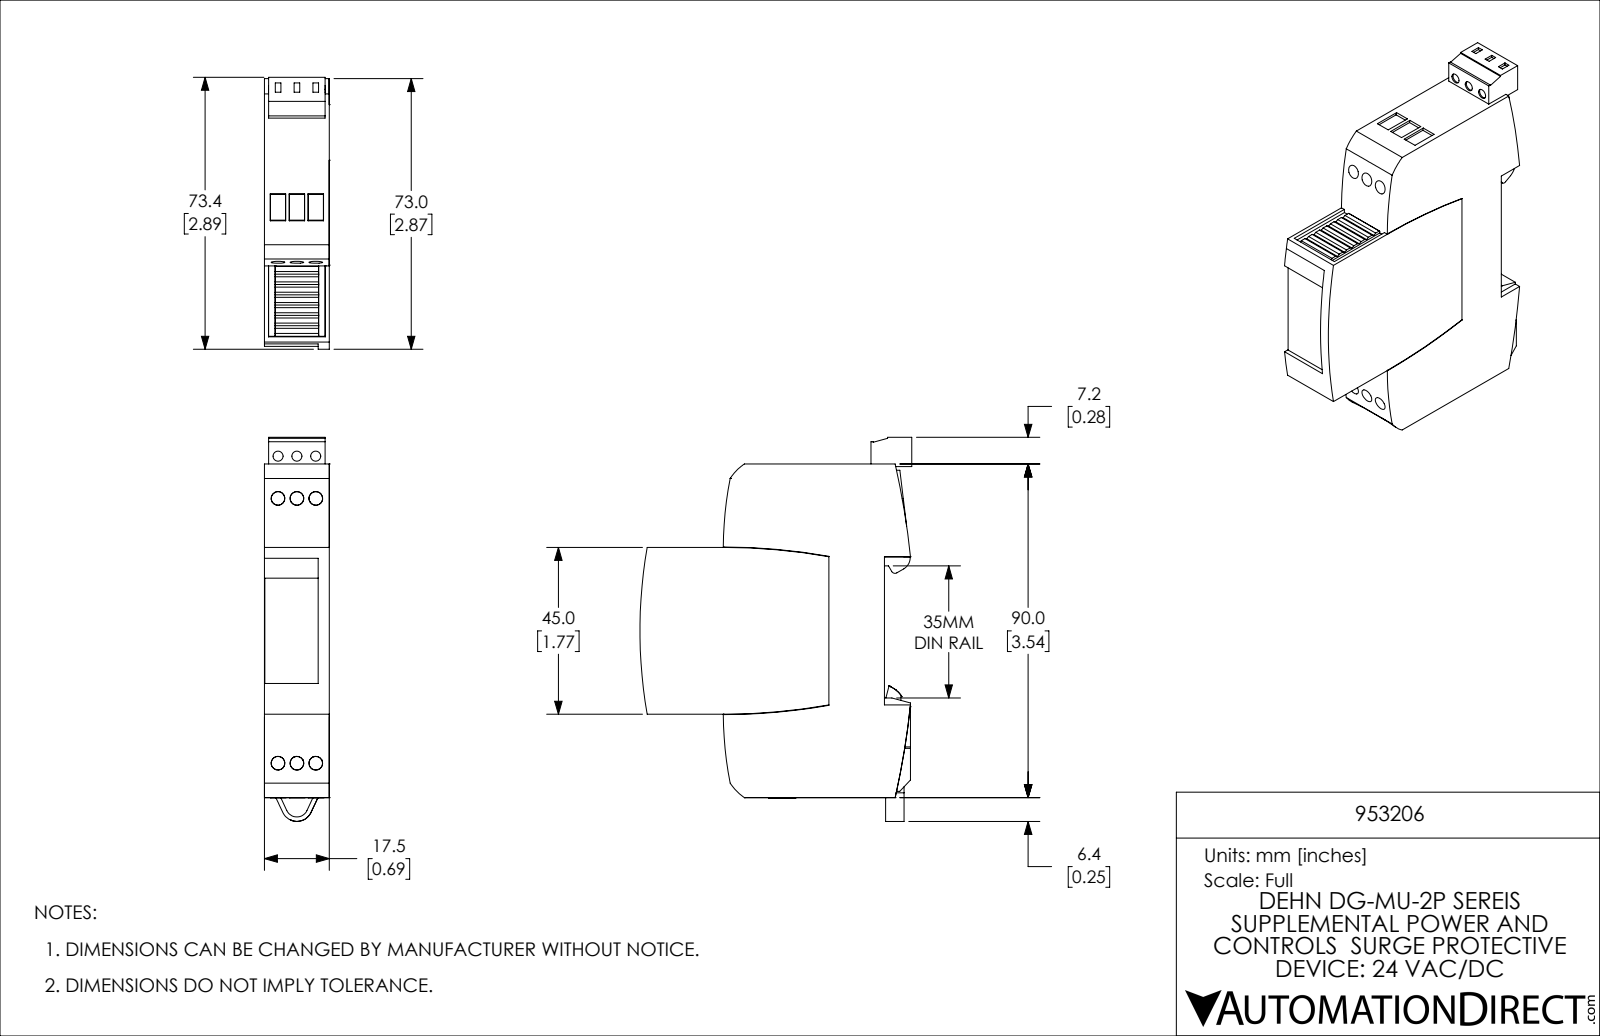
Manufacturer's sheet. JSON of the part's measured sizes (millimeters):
{"part_name": "953206", "step_written_by": "SolidWorks 2019 (CONFIG_CONTROL_DESIGN)", "units": "millimeters", "bodies": {"solids": 1, "faces": 255, "planar": 198, "cylindrical": 38, "other": 19}, "overall_size": [103.6, 73.4, 17.5], "volume_mm3": 89060, "surface_area_mm2": 17550, "round_holes": [[2.7, 3]], "partial_cylinders_radius": [[163.8, 2], [163.8, 2], [1, 1], [2.5, 1], [3, 1], [3.5, 1], [100, 1], [100.1, 1]], "face_to_face_distances": [17.5, 17.4, 90, 0.4, 17.1, 64, 7, 71, 22.8, 67.2], "hole_center_spacings": [5.1, 10.2]}
